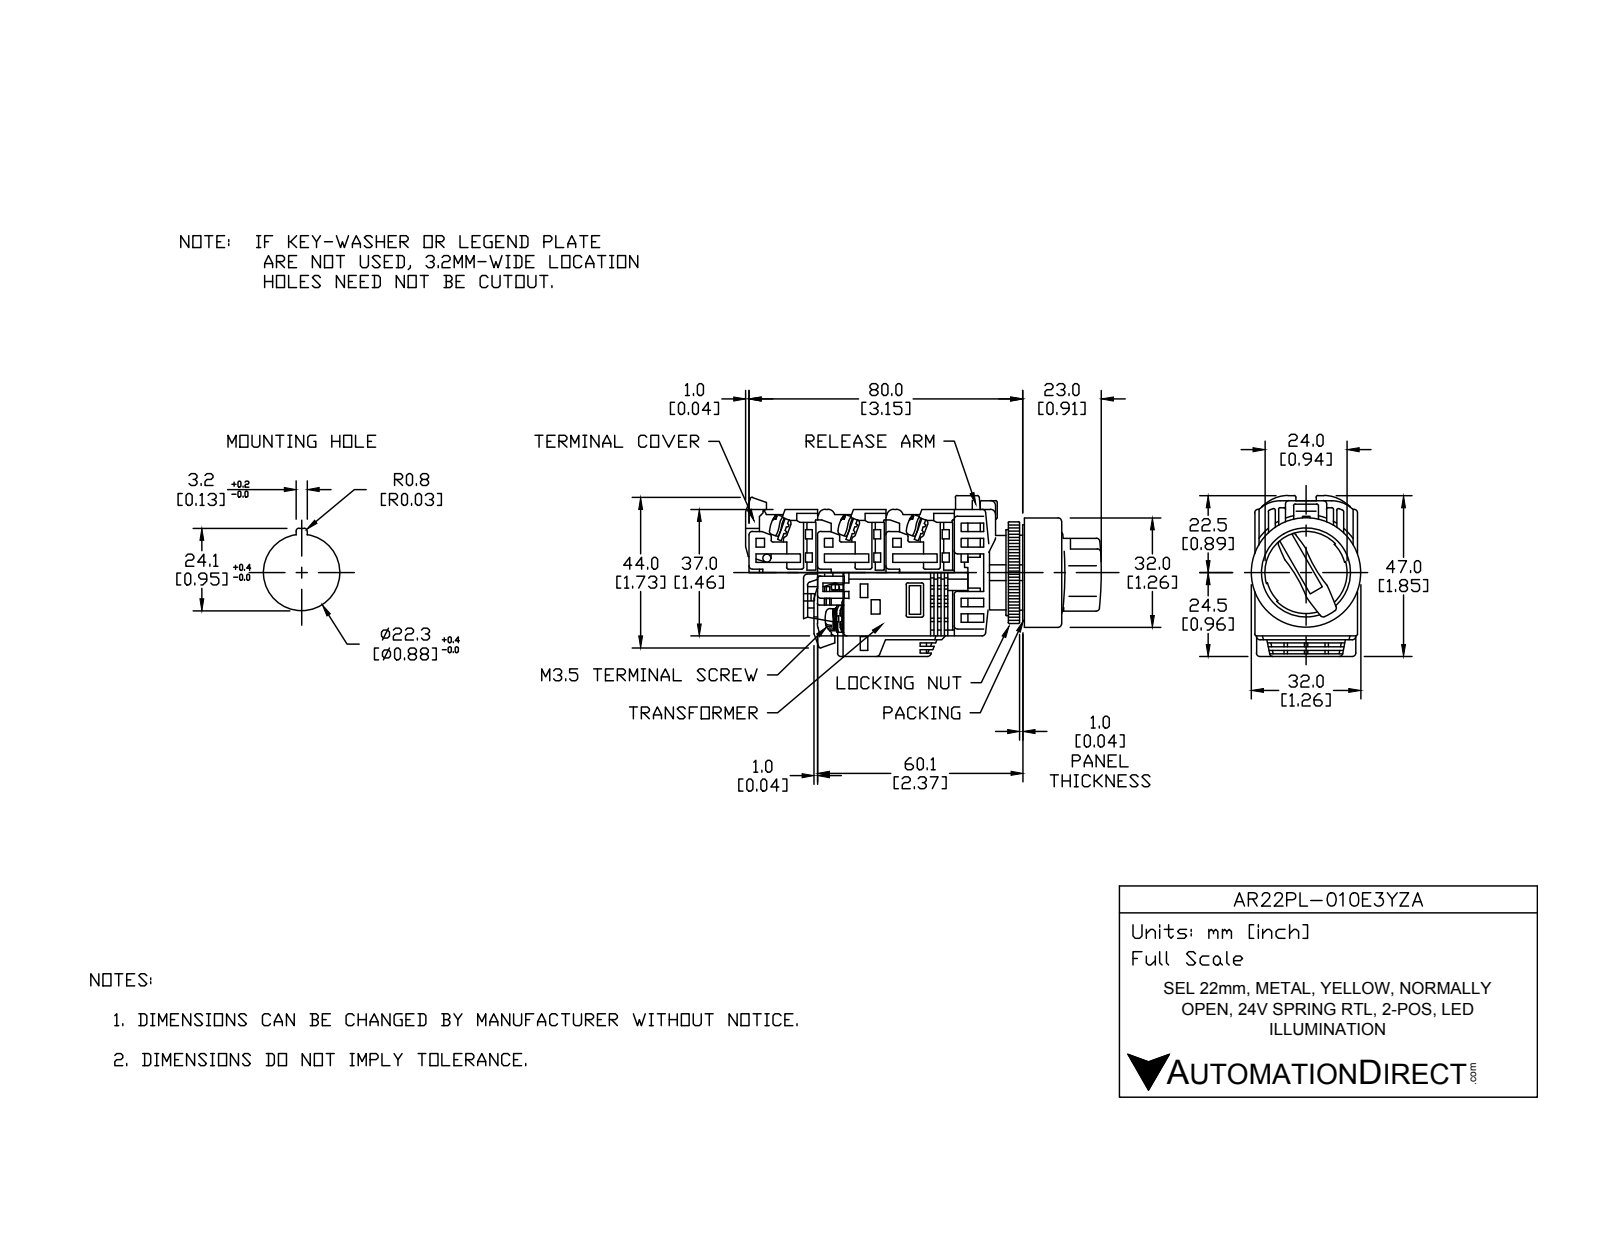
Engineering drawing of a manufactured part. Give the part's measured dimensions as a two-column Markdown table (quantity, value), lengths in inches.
| quantity | value |
| --- | --- |
| part name | AR22PL-010E3YZA |
| STEP written by | SolidWorks 2017 (AUTOMOTIVE_DESIGN) |
| units | inches |
| bodies | 18 solids, 462 faces (317 planar, 118 cylindrical, 27 other) |
| overall size | 2.539 × 1.725 × 1.26 |
| volume | 2.351 in³ |
| surface area | 38.49 in² |
| round holes (diameter × count) | 0.858 × 1, 0.866 × 1, 0.984 × 1, 1.22 × 1 |
| round bosses / shafts (diameter × count) | 0.197 × 4, 1.26 × 1, 1.201 × 1, 1.173 × 1, 0.945 × 1, 0.856 × 1, 0.669 × 1 |
| partial cylindrical surfaces (radius × count) | 0.02 × 39, 0.069 × 8, 0.039 × 6, 0.197 × 4, 0.157 × 2, 0.472 × 1, 0.653 × 1, 0.693 × 1 |
| main face-to-face distances | 0.039, 0.709, 0.118, 1.122, 1.909, 0.787, 1.142, 0.02, 0.079, 1.22 |
